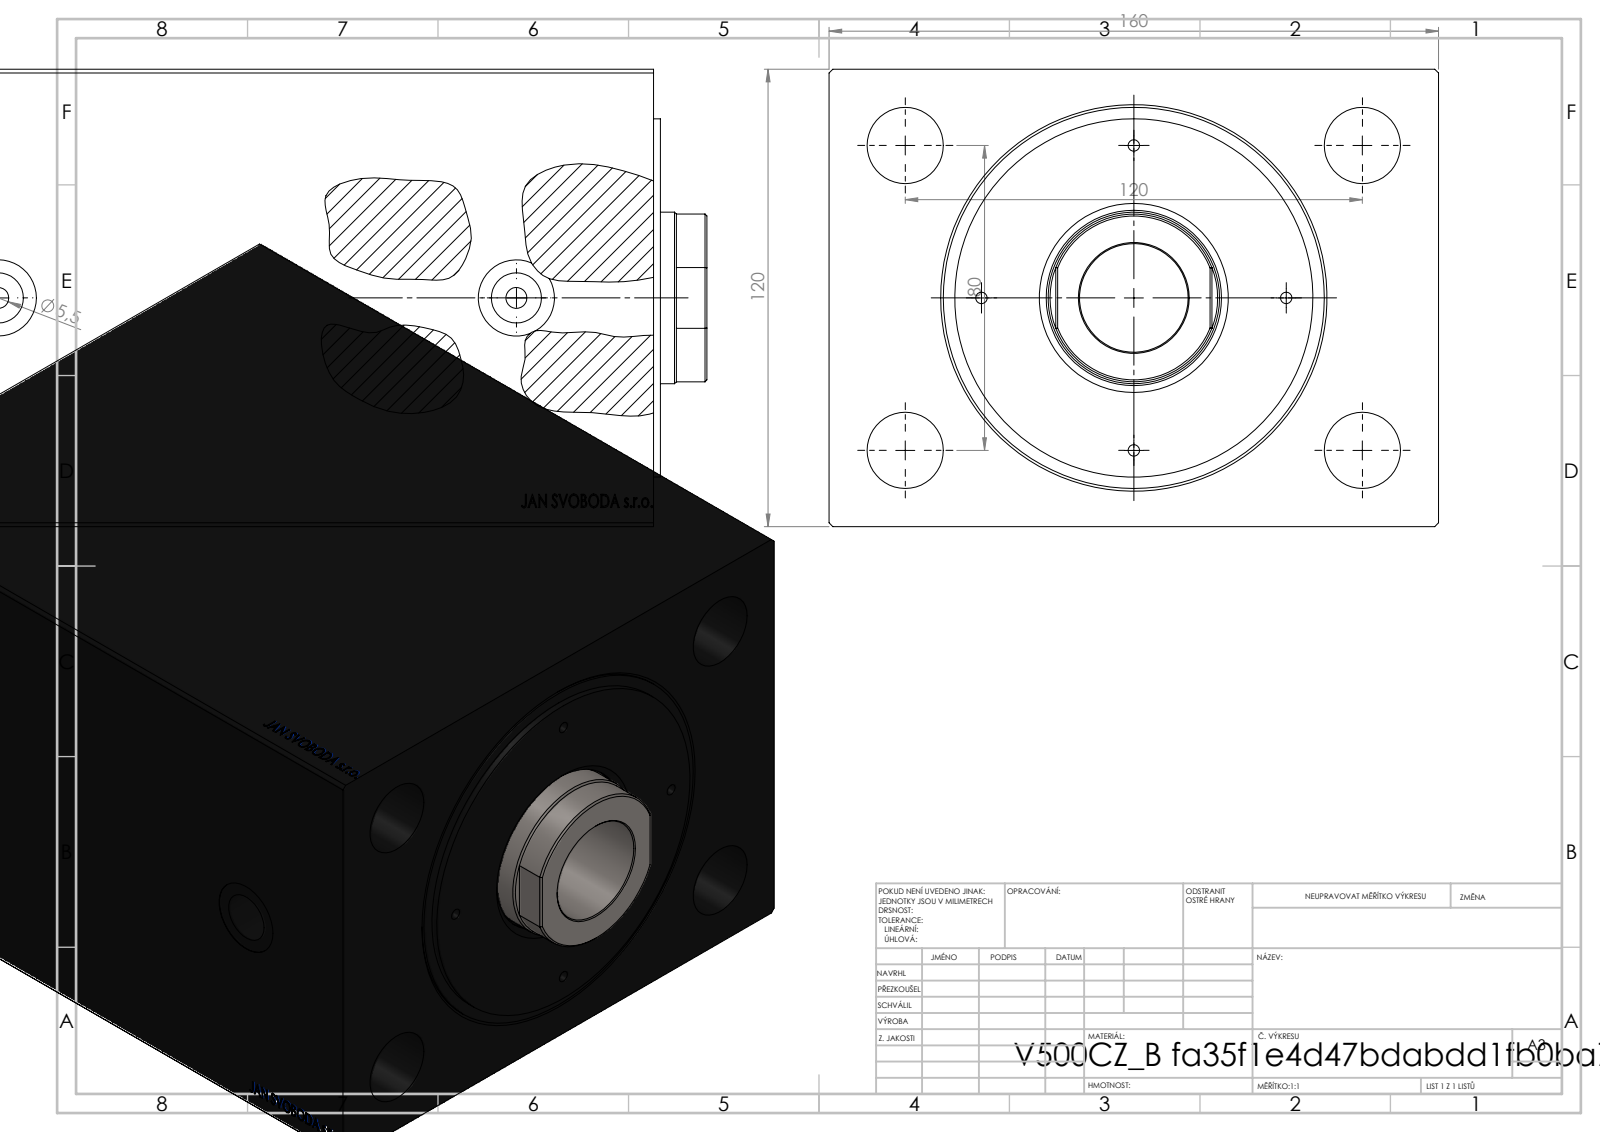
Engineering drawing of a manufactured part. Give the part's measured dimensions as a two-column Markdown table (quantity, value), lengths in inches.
| quantity | value |
| --- | --- |
| part name | V500CZ_B_VC; V500CZ |
| STEP written by | SolidWorks 2019 (CONFIG_CONTROL_DESIGN) |
| units | inches |
| bodies | 3 solids, 874 faces (400 planar, 58 cylindrical, 416 other) |
| overall size | 8.031 × 6.299 × 4.724 |
| volume | 215.1 in³ |
| surface area | 488 in² |
| round holes (diameter × count) | 0.787 × 6, 0.118 × 4, 0.217 × 2, 0.518 × 2, 1.122 × 1, 1.417 × 1, 1.772 × 1, 1.811 × 1, 3.15 × 1, 3.937 × 1 |
| round bosses / shafts (diameter × count) | 3.701 × 1 |
| partial cylindrical surfaces (radius × count) | 0.866 × 1 |
| main face-to-face distances | 4.724, 6.299, 7.48, 6.535, 0.945, 4.331, 2.205, 3.15, 0.071, 4.402 |
| hole center spacings | 1.575, 1.761, 2.227, 2.362, 2.839, 3.15, 3.937, 4.24 |
